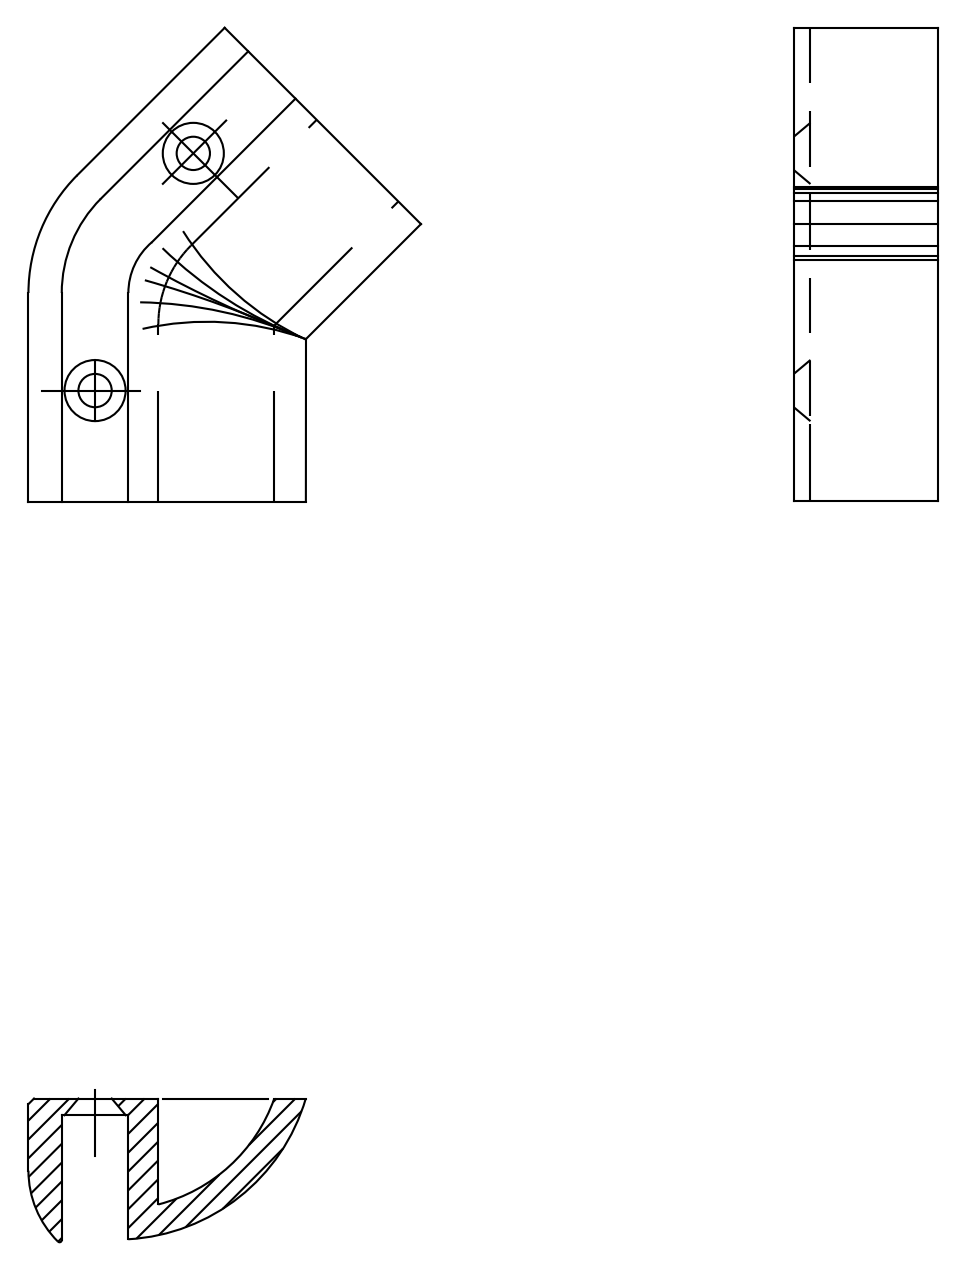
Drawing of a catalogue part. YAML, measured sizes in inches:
step_written_by: "THINKDESIGN (CONFIG_CONTROL_DESIGN)"
units: inches
bodies: {solids: 1, faces: 32, planar: 12, cylindrical: 11, other: 9}
overall_size: [1.68, 1.391, 0.509]
volume: 0.451
surface_area: 6.256
partial_cylinders:
  - {radius: 0.012, count: 4}
  - {radius: 0.354, count: 2}
  - {radius: 0.697, count: 2}
  - {radius: 0.236, count: 1}
  - {radius: 0.472, count: 1}
  - {radius: 0.591, count: 1}
face_to_face_distances: [0.236, 0.118, 0.354, 0.059]
